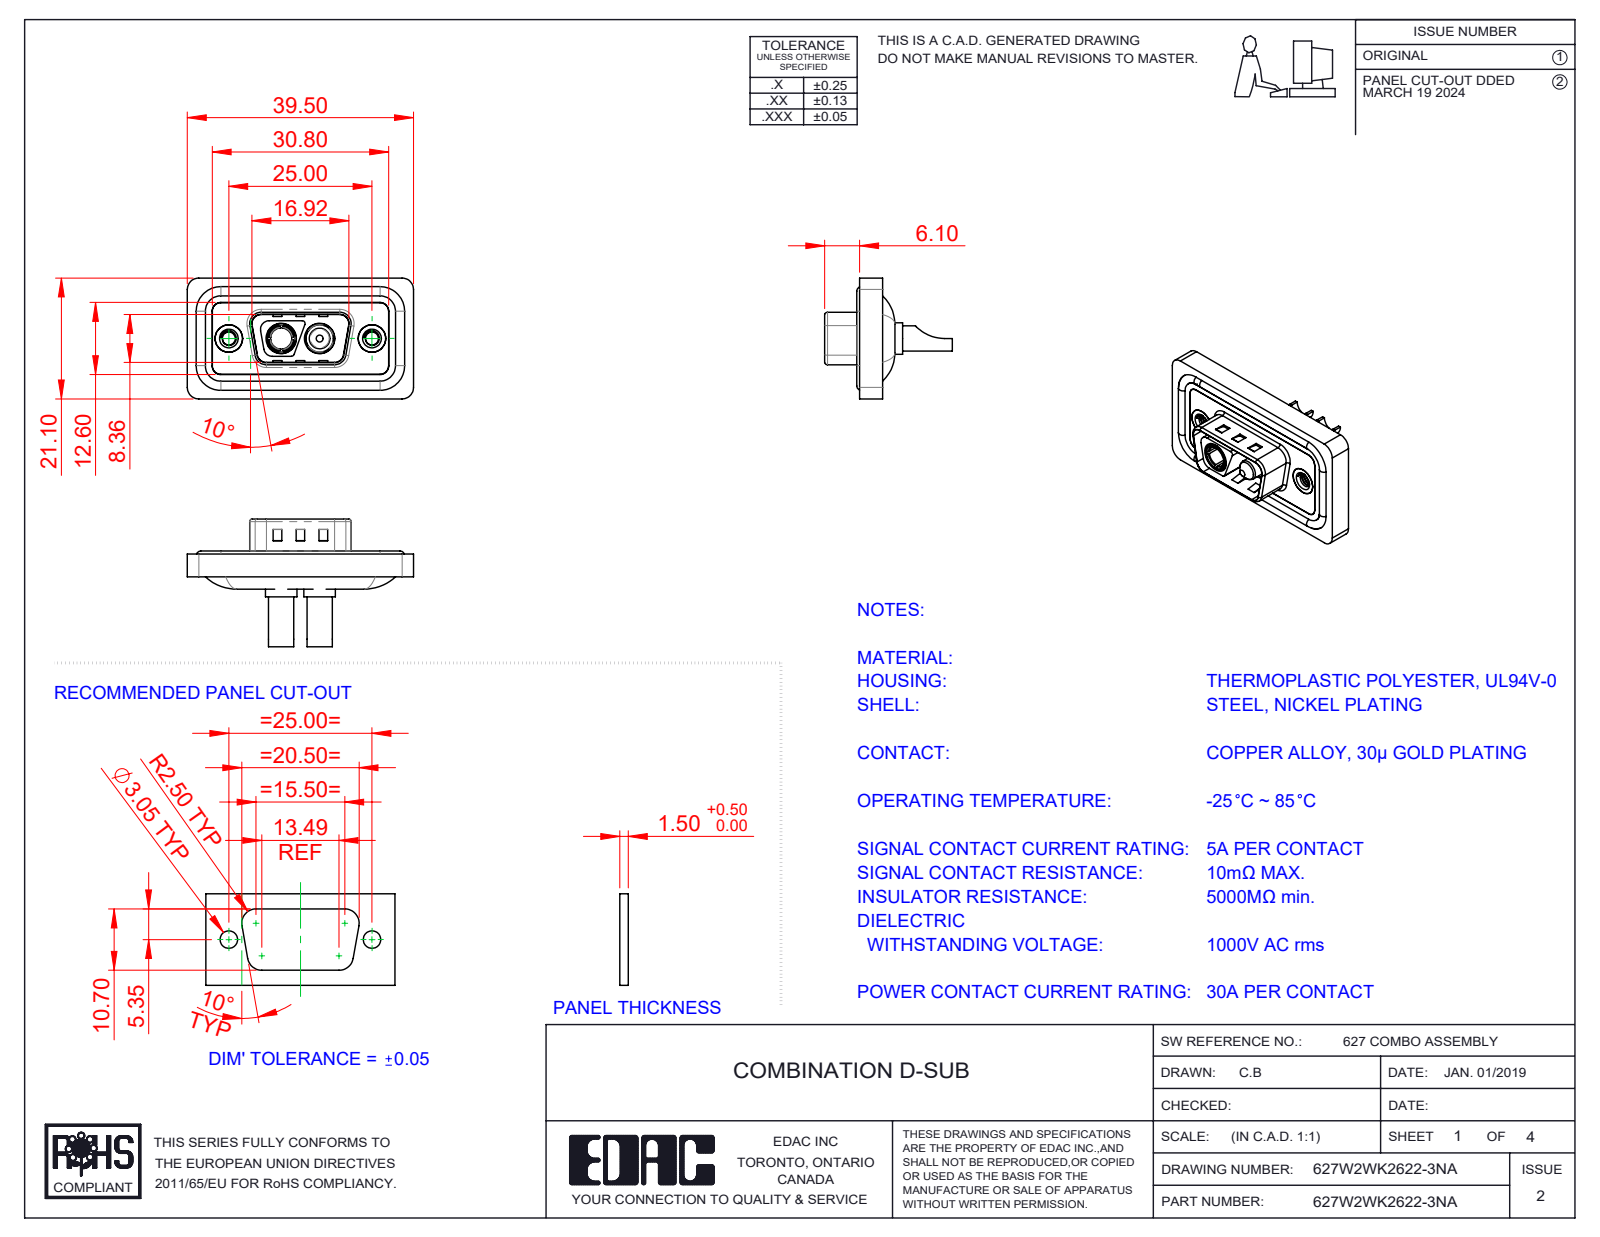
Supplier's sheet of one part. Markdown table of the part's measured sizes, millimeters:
| quantity | value |
| --- | --- |
| part name | 627W2WK2622-3NA; 627Combo Waterproof Housing_09 Contacts; Power Socket_30A SC; 627Combo Threaded Rivet_A (+4 more) |
| STEP written by | SolidWorks 2023 (CONFIG_CONTROL_DESIGN) |
| units | millimeters |
| bodies | 11 solids, 544 faces (195 planar, 235 cylindrical, 114 other) |
| overall size | 39.5 × 22.3 × 21.1 |
| volume | 4 604 mm³ |
| surface area | 7 555 mm² |
| round holes (diameter × count) | 2.26 × 2, 3.5 × 2, 4 × 2, 4.8 × 2, 4.85 × 2, 5 × 2, 5.3 × 2, 3.7 × 1 |
| round bosses / shafts (diameter × count) | 1.6 × 4, 5.5 × 2, 5.2 × 2, 4.9 × 2, 4.75 × 2, 4.4 × 2, 3.75 × 2, 4.96 × 1 |
| partial cylindrical surfaces (radius × count) | 1.5 × 24, 2 × 18, 0.5 × 10, 1.6 × 8, 0.25 × 4, 0.6 × 4, 0.65 × 4, 0.9 × 4 |
| main face-to-face distances | 0.4, 1.1, 2.9, 0.5, 3.1, 1.6, 1.5, 2.5, 1.8, 3.2 |
| hole center spacings | 9.14, 15.86, 6.72, 25 |
